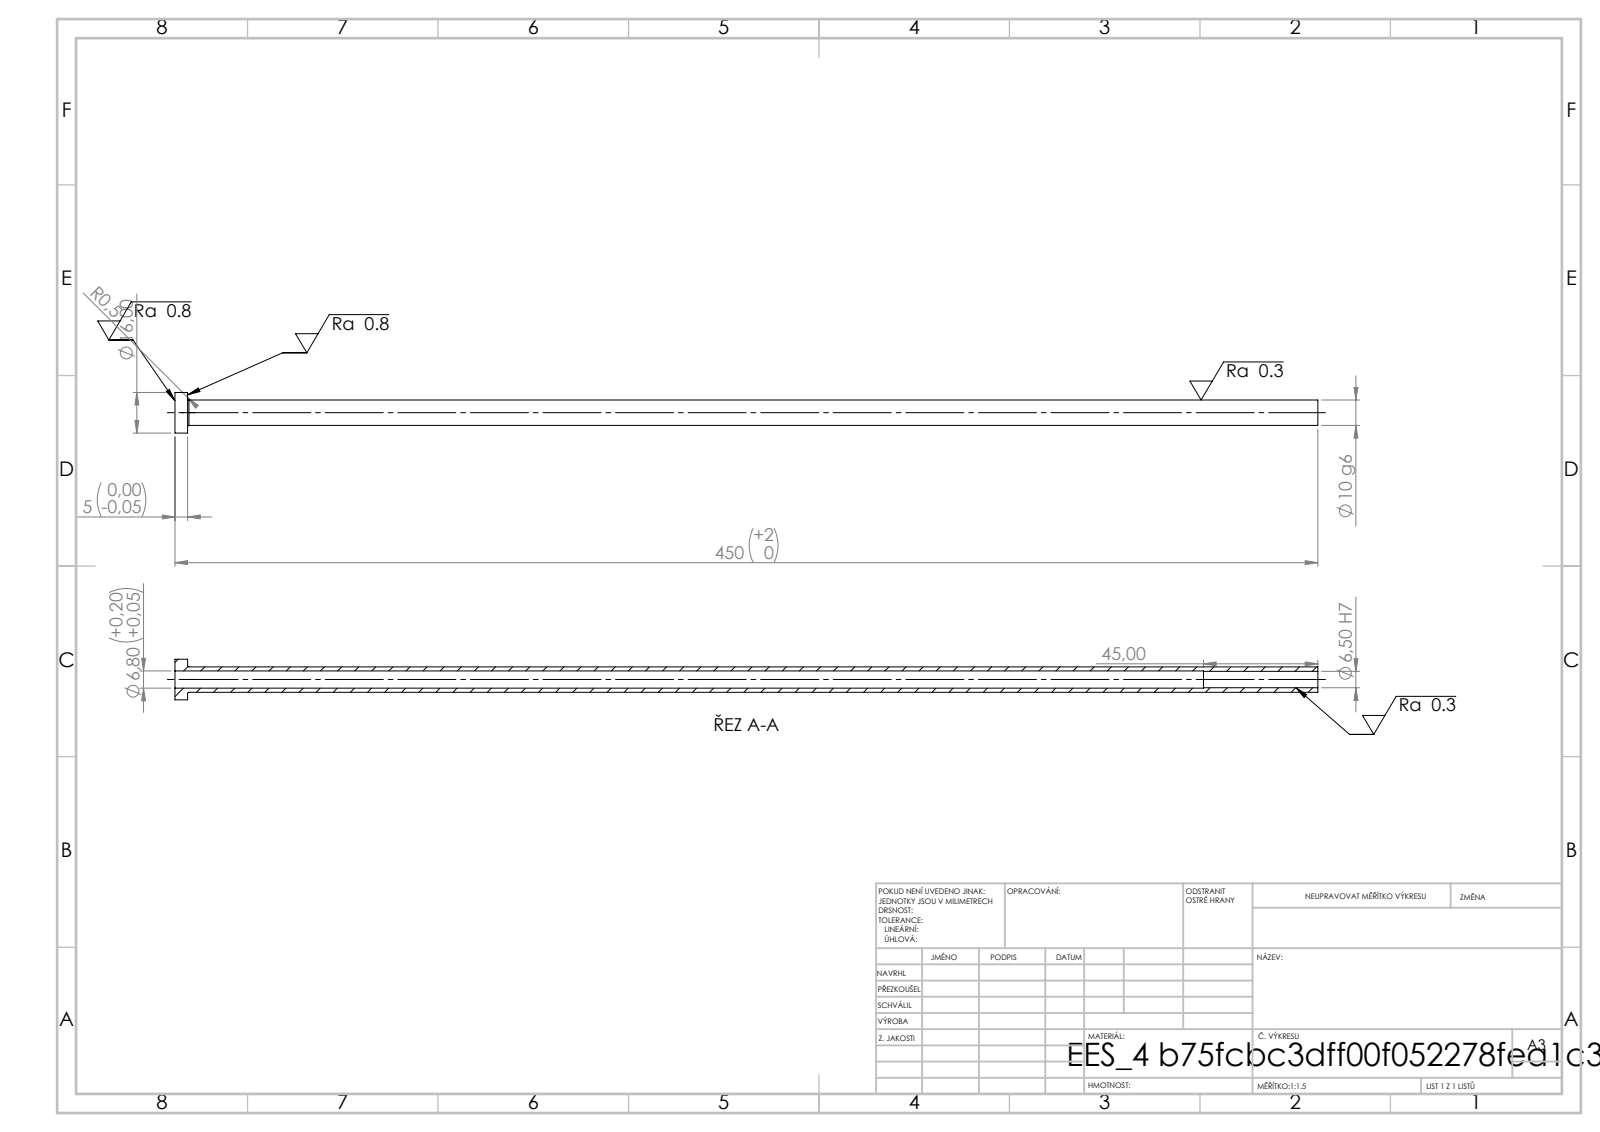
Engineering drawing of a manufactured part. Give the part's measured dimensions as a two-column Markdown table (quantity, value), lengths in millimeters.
| quantity | value |
| --- | --- |
| STEP written by | SolidWorks 2019 (CONFIG_CONTROL_DESIGN) |
| units | millimeters |
| bodies | 1 solid, 14 faces (4 planar, 8 cylindrical, 2 other) |
| overall size | 450 × 16 × 16 |
| volume | 19 756 mm³ |
| surface area | 24 131 mm² |
| round holes (diameter × count) | 6.5 × 1, 6.8 × 1 |
| round bosses / shafts (diameter × count) | 16 × 1, 10 × 1 |
| main face-to-face distances | 5, 450, 445, 405, 400, 45 |
